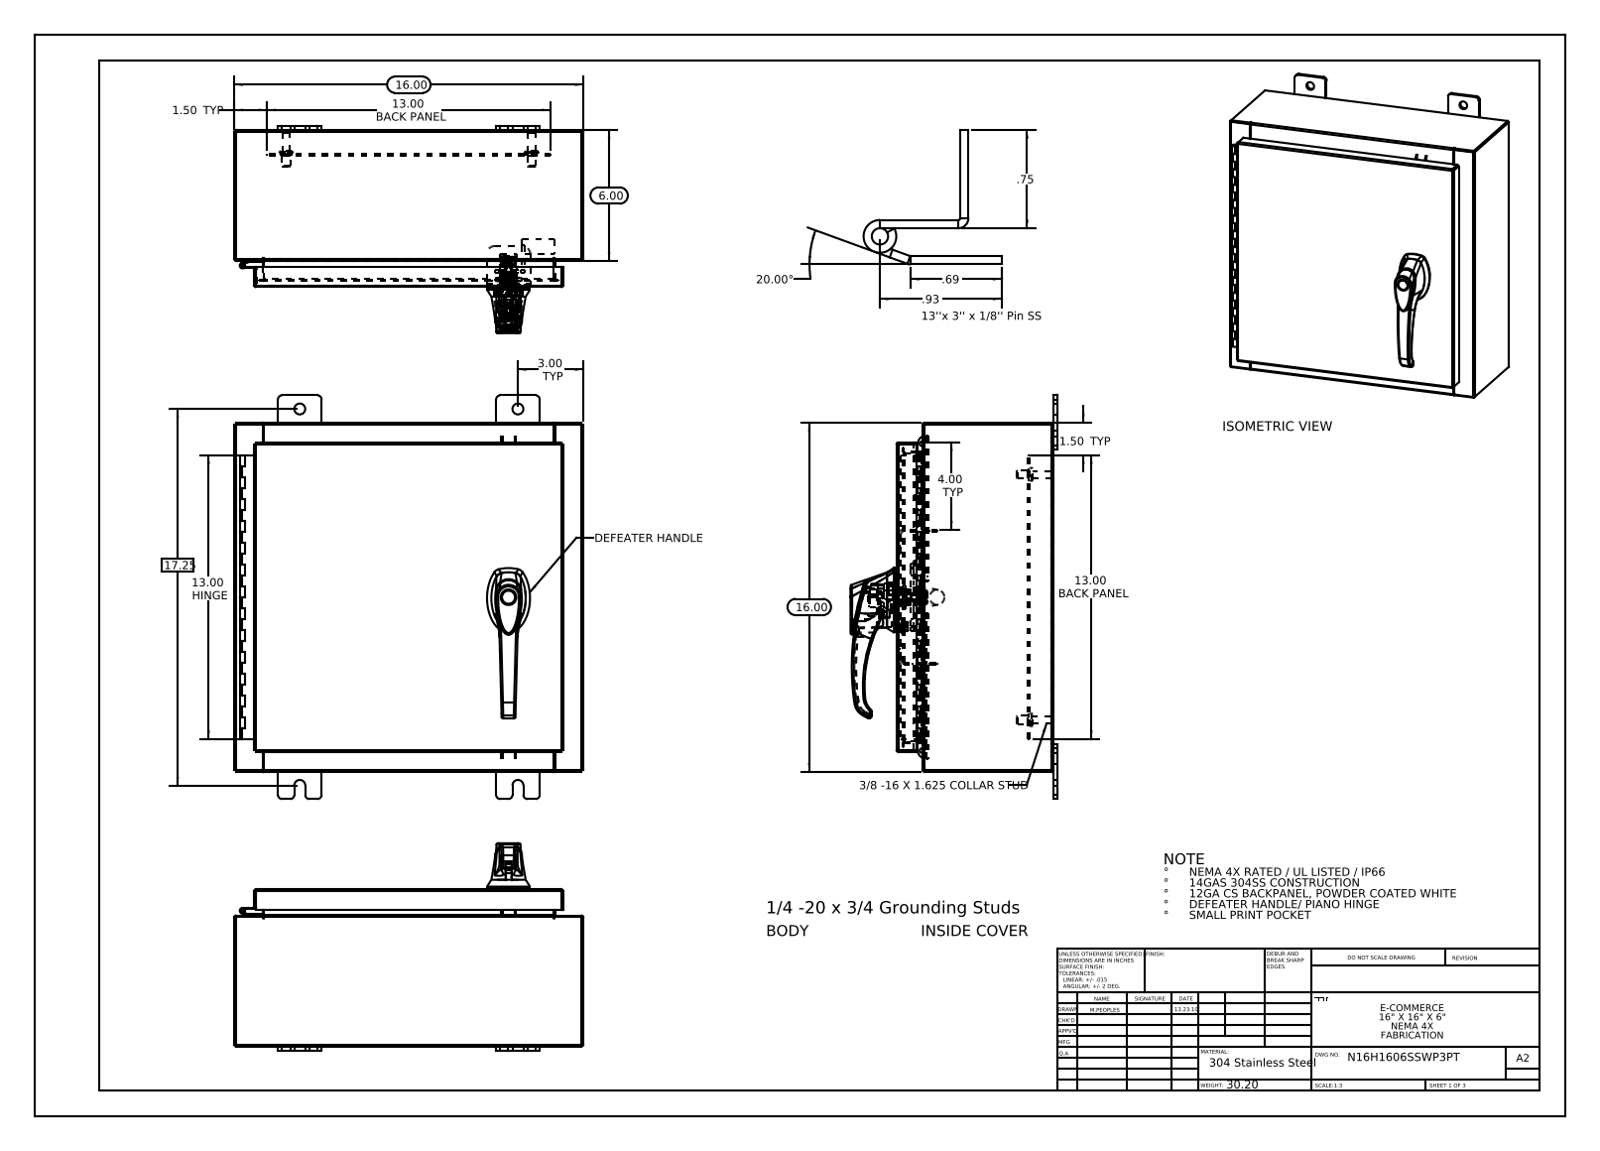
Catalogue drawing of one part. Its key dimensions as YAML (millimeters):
part_name: "N16H1606SSWP3PT Mounting Feet; 012103_012102; N16H1606SSWP3PT Backpanel; 033060_032151 (+8 more)"
step_written_by: "SolidWorks 2013 (CONFIG_CONTROL_DESIGN)"
units: millimeters
bodies: {solids: 37, faces: 2290, planar: 775, cylindrical: 817, other: 698}
overall_size: [469.9, 406.4, 241.2]
volume: 1783000
surface_area: 1719000
round_holes:
  - {diameter: 12.7, count: 8}
  - {diameter: 6.4, count: 4}
  - {diameter: 3.5, count: 3}
  - {diameter: 4.1, count: 3}
  - {diameter: 2, count: 2}
  - {diameter: 5.2, count: 2}
  - {diameter: 8, count: 2}
  - {diameter: 11.1, count: 2}
  - {diameter: 3.2, count: 1}
  - {diameter: 3.2, count: 1}
  - {diameter: 5, count: 1}
  - {diameter: 7, count: 1}
round_bosses_or_shafts:
  - {diameter: 15.9, count: 4}
  - {diameter: 9.5, count: 4}
  - {diameter: 8.4, count: 4}
  - {diameter: 4, count: 4}
  - {diameter: 3.6, count: 4}
  - {diameter: 8, count: 3}
  - {diameter: 6, count: 3}
  - {diameter: 30, count: 1}
partial_cylinders:
  - {radius: 3, count: 37}
  - {radius: 0.2, count: 33}
  - {radius: 4.8, count: 24}
  - {radius: 0.3, count: 20}
  - {radius: 2.2, count: 18}
  - {radius: 1, count: 15}
  - {radius: 0.7, count: 12}
  - {radius: 0.2, count: 6}
face_to_face_distances: [1.9, 181, 404.5, 179.1, 182.9, 402.6, 406.4, 25.4, 2.6, 27.3]
hole_center_spacings: [94.2, 7.5, 15.9, 21.4, 31.8, 33.4, 33.5, 37.7]
